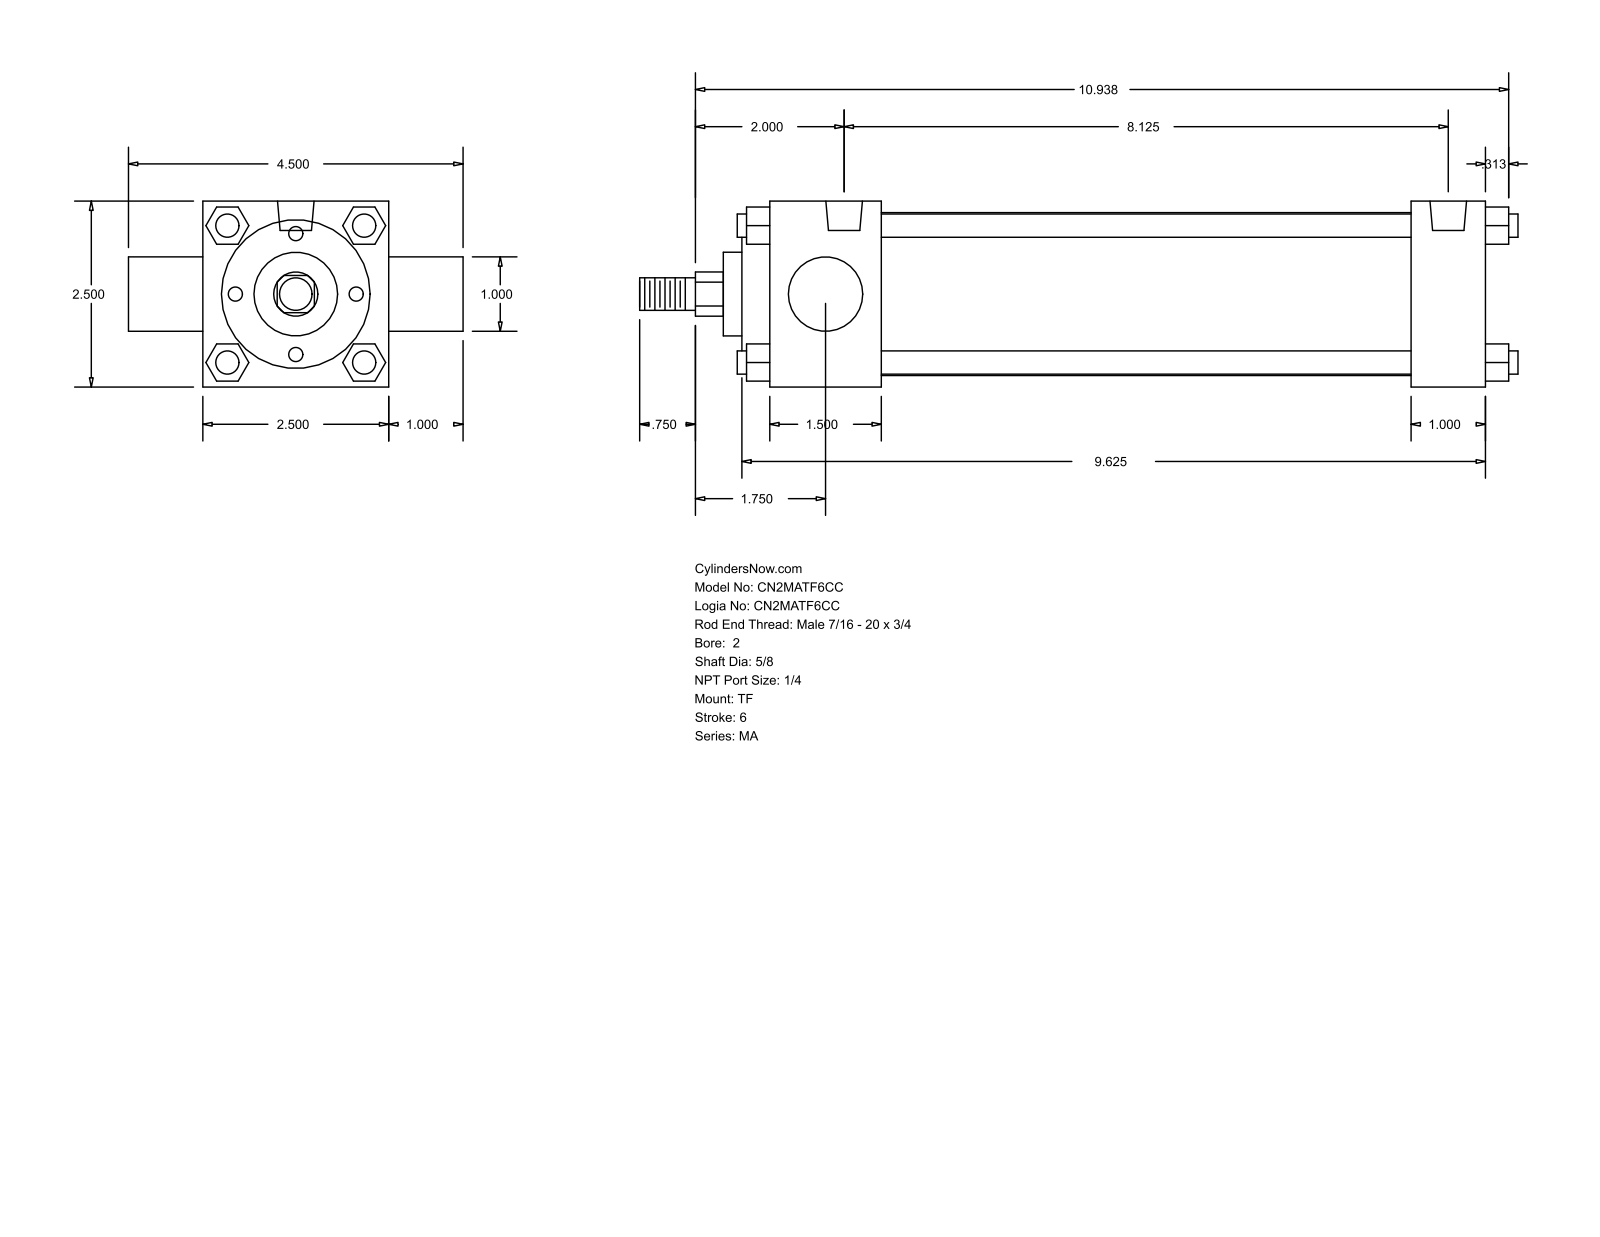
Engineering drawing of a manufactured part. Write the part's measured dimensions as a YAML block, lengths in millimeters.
part_name: "MA_TF__0200_0.625"
step_written_by: "GSSL Pune (CONFIG_CONTROL_DESIGN)"
units: millimeters
bodies: {solids: 0, faces: 122, planar: 93, cylindrical: 29, other: 0}
overall_size: [300.04, 114.3, 63.5]
round_holes:
  - {diameter: 7.94, count: 3}
  - {diameter: 12.49, count: 2}
round_bosses_or_shafts:
  - {diameter: 7.94, count: 4}
  - {diameter: 55.63, count: 1}
  - {diameter: 50.8, count: 1}
  - {diameter: 28.57, count: 1}
  - {diameter: 25.4, count: 1}
  - {diameter: 15.88, count: 1}
  - {diameter: 11.11, count: 1}
partial_cylinders:
  - {radius: 7.54, count: 1}
face_to_face_distances: [63.5, 38.1, 12.7, 244.48, 219.07, 180.97, 206.38, 25.41, 9.52, 47.62]
hole_center_spacings: [206.38]
